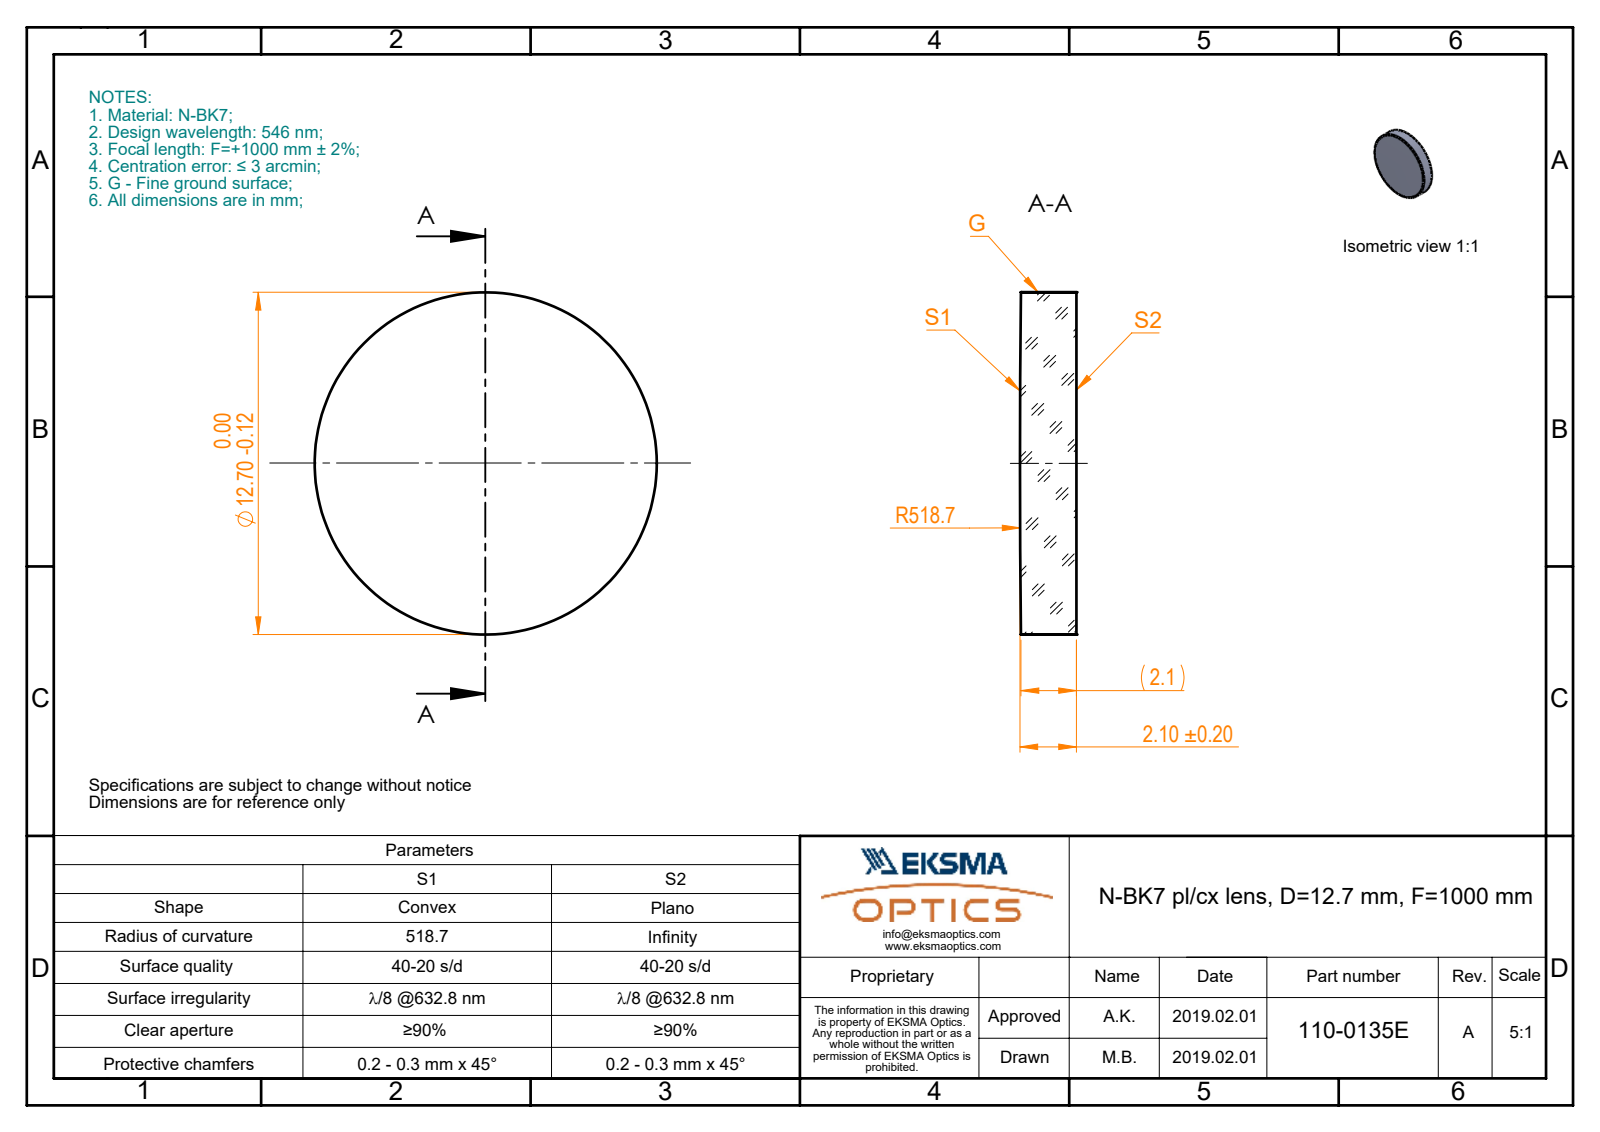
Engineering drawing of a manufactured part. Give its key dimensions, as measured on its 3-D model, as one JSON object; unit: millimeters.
{"part_name": "110-0135E BK7 pl-cx 12.7 F1000", "step_written_by": "SolidWorks 2017 (CONFIG_CONTROL_DESIGN)", "units": "millimeters", "bodies": {"solids": 1, "faces": 5, "planar": 1, "cylindrical": 2, "other": 2}, "overall_size": [12.7, 12.7, 2.1], "volume_mm3": 264, "surface_area_mm2": 336, "round_bosses_or_shafts": [[12.7, 1]]}
